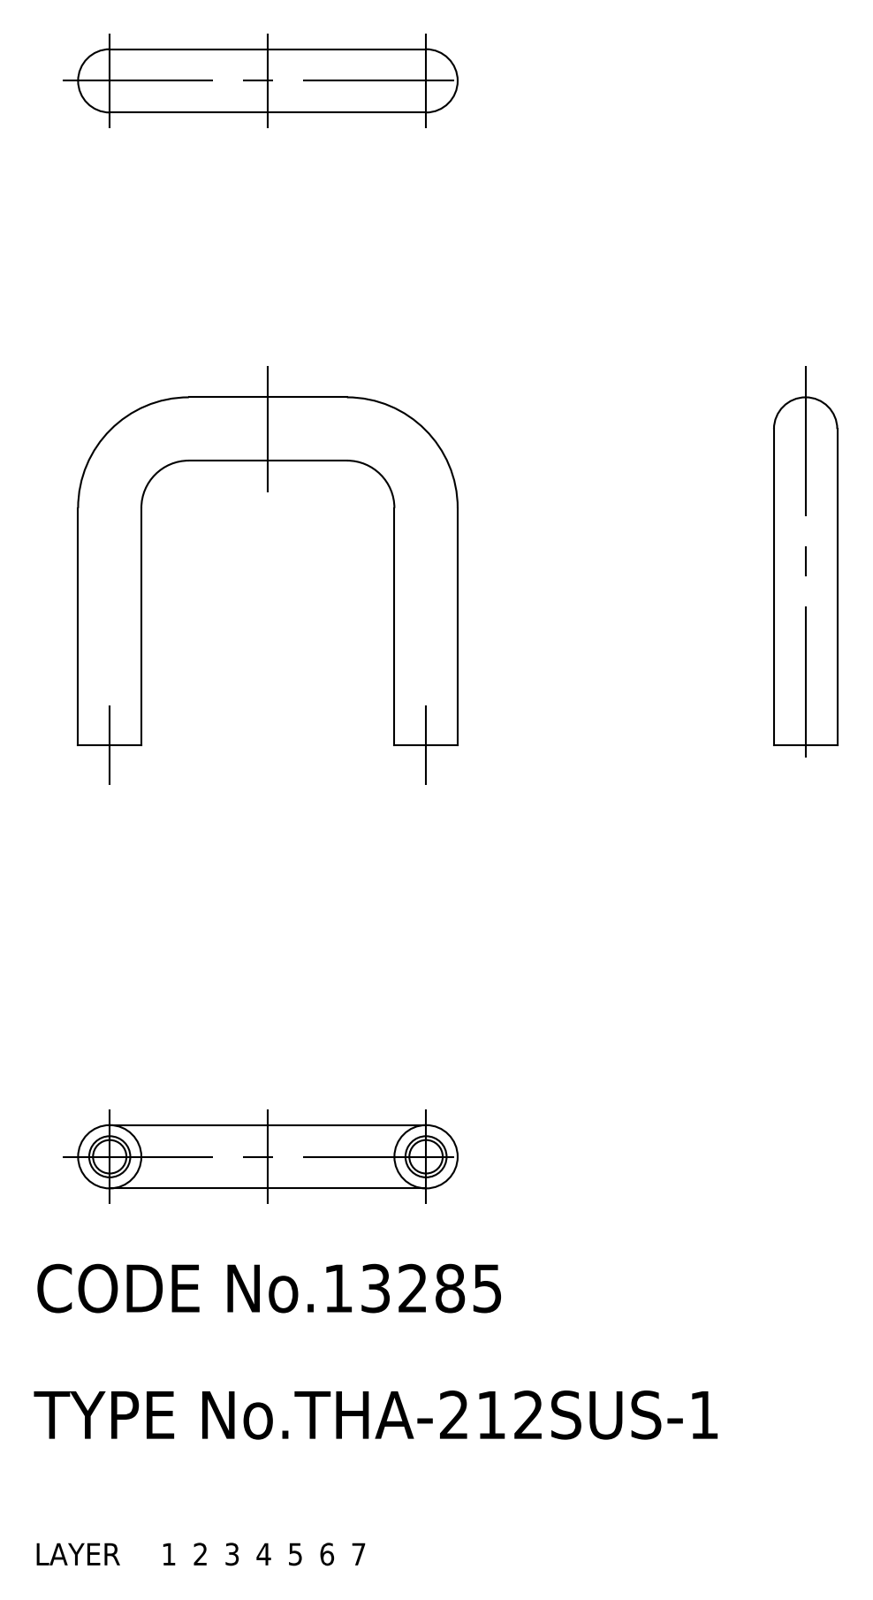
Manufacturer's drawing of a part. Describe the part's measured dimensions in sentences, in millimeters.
The part is named "pull". Its 3-D file was written by "CADfix (AUTOMOTIVE_DESIGN)". It is 1 solid with 18 faces: 0 planar, 0 cylindrical and 18 other. Overall it measures 24 by 22 by 4 millimeters. Its volume is 595 cubic millimeters and its surface area 889 square millimeters.
